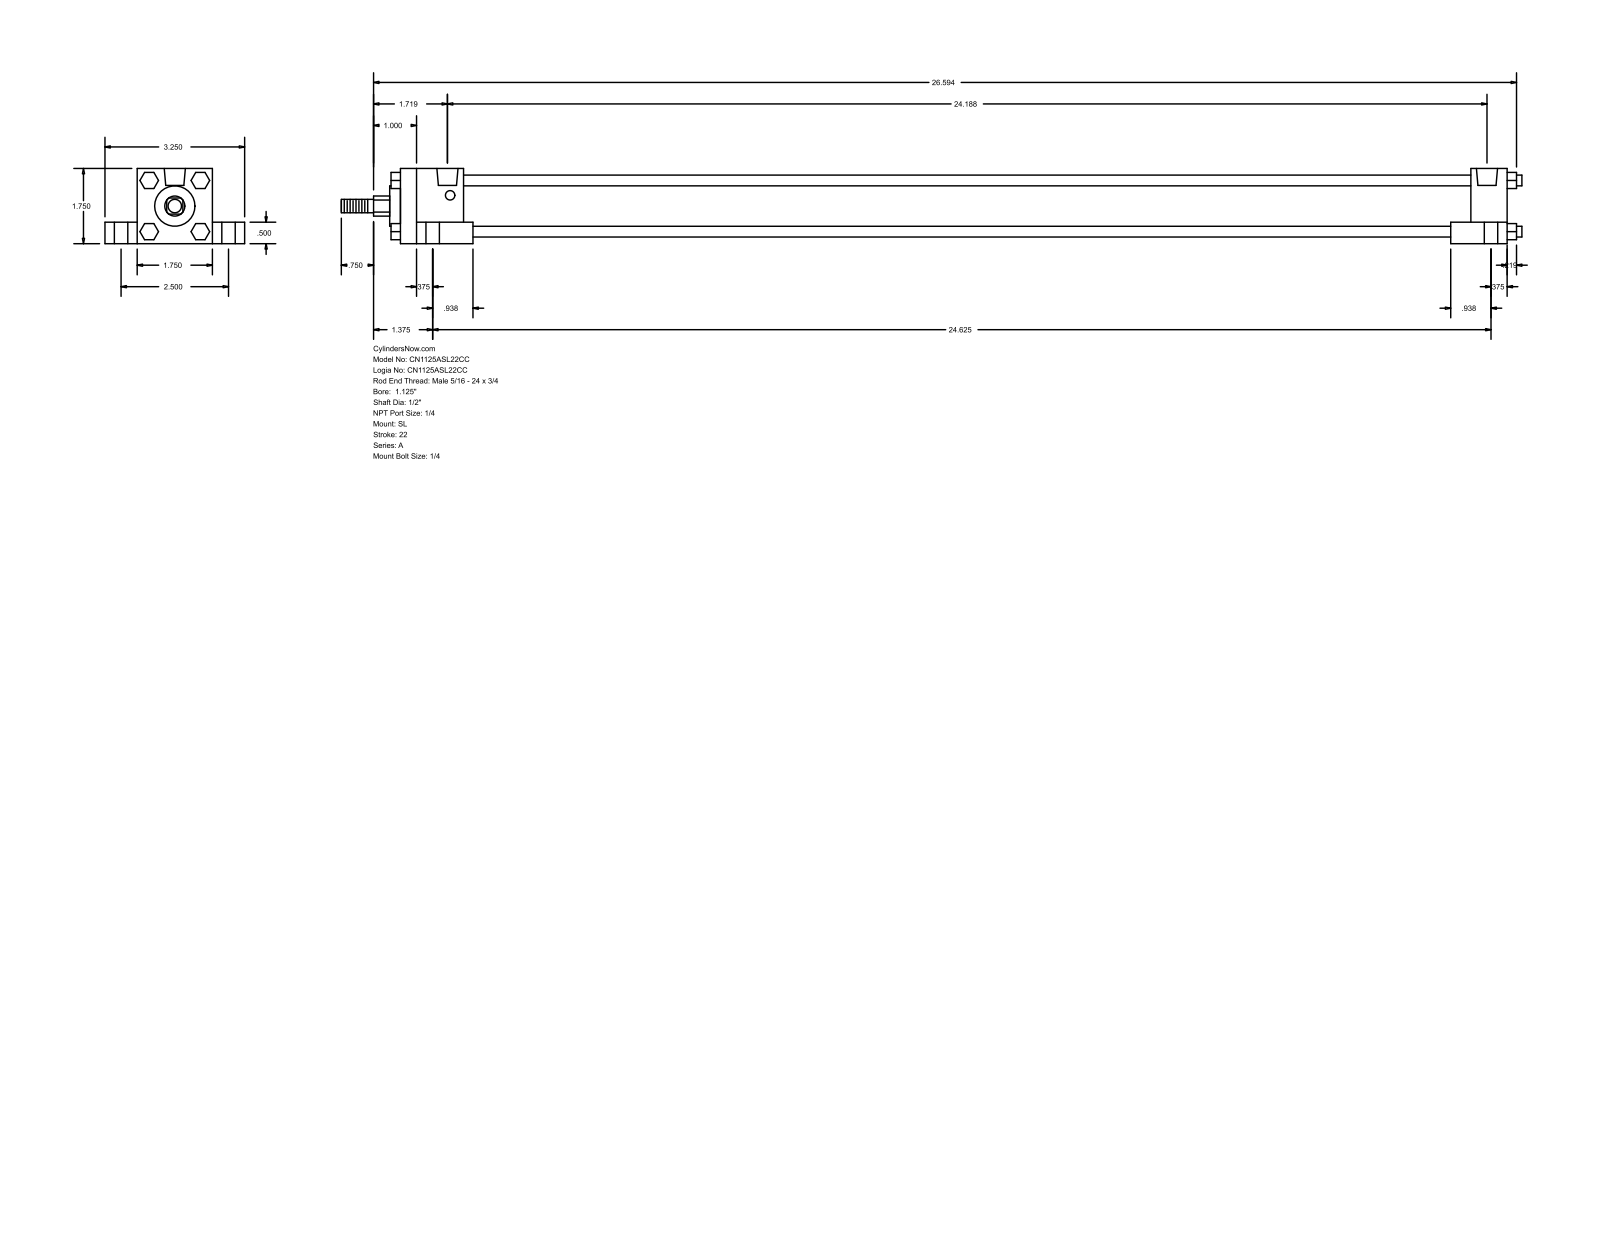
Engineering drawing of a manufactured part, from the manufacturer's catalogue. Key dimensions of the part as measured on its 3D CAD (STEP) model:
Part name (STEP PRODUCT): A_SL__0112_0.5
STEP written by: GSSL Pune (CONFIG_CONTROL_DESIGN)
Units: millimetres
Bodies: 0 solids, 150 faces (114 planar, 36 cylindrical, 0 other)
Overall size (bounding box): 697.71 × 82.55 × 44.45
Round holes (diameter × count): ⌀5.56 ×4, ⌀7.94 ×4, ⌀14.29 ×4, ⌀12.49 ×2
Round bosses / shafts (diameter × count): ⌀6.35 ×4, ⌀31.88 ×1, ⌀23.81 ×1, ⌀12.7 ×1, ⌀7.94 ×1
Partial cylindrical surfaces — rounded edges, fillets, slot ends (radius × count): R5.94 ×1
Main face-to-face distances: 44.46, 31.76, 12.7, 19.04, 63.5, 616.74, 654.04, 632.61, 21.43, 37.3
Hole centre spacings: 31.84, 32, 32.93, 33.39, 63.5, 611.19, 615.98, 617.56
